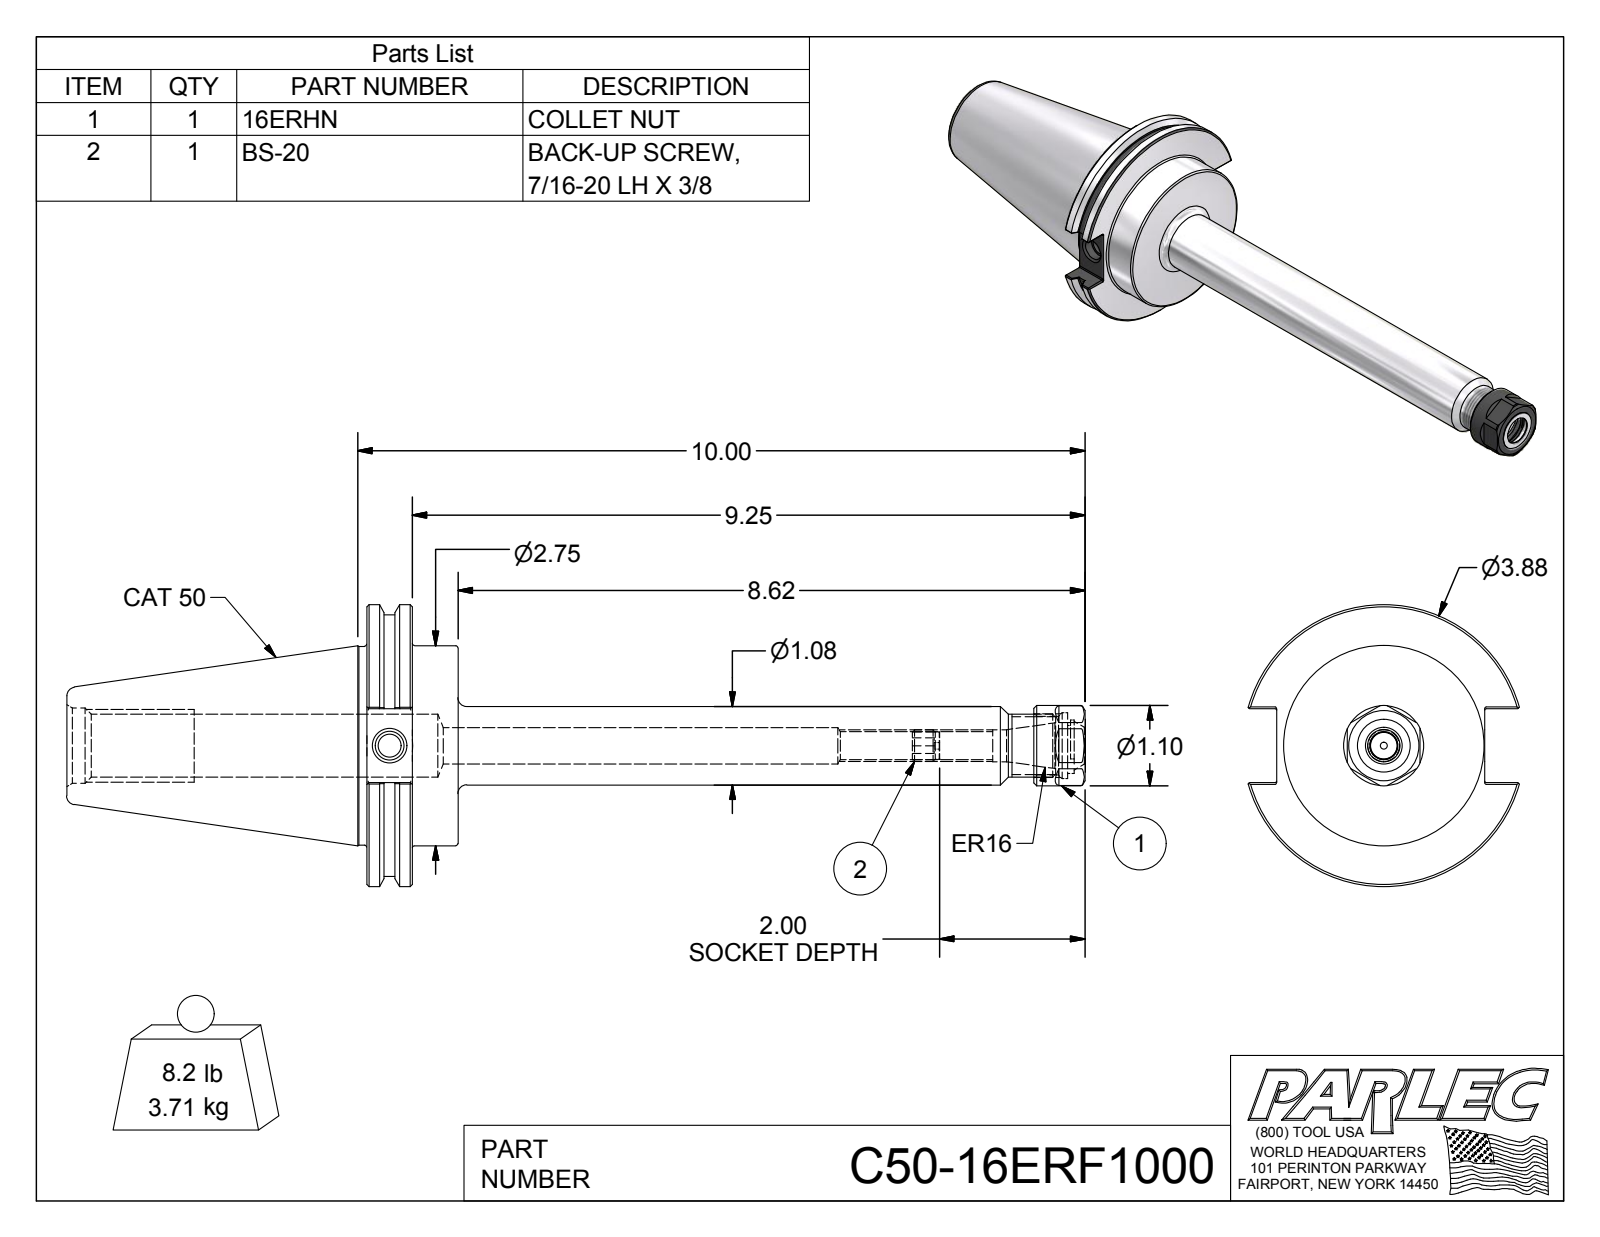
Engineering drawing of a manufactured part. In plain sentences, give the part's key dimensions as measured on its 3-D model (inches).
The part is named "C50-16ER10-1; 16ERHN; BS-20; C50-16ERF1000". Its 3-D file was written by "Autodesk Inventor 2016 (AUTOMOTIVE_DESIGN)". It is 3 solids with 145 faces: 59 planar, 39 cylindrical and 47 other. Overall it measures 14 by 3.875 by 3.729 inches. Its volume is 29.02 cubic inches and its surface area 120.9 square inches. Round holes: 1 of diameter 0.09, 1 of diameter 0.315, 1 of diameter 0.383, 1 of diameter 0.399, 1 of diameter 0.44, 1 of diameter 0.488, 1 of diameter 0.5, 1 of diameter 0.67, 1 of diameter 0.807, 1 of diameter 0.865, 1 of diameter 0.906, 1 of diameter 1.038. Round bosses or shafts: 1 of diameter 3.875, 1 of diameter 3.594, 1 of diameter 2.75, 1 of diameter 2.73, 1 of diameter 1.102, 1 of diameter 1.08, 1 of diameter 0.866, 1 of diameter 0.432. Partial cylindrical surfaces (rounded edges, fillets, slot ends): 12 of radius 0.02, 1 of radius 0.285, 1 of radius 0.354. The main face-to-face distances are 1.255, 0.625, 0.63, 9.875, 9.25, 8.62, 0.99, 4.125, 4.75, 5.38. The hole center spacings are 0.06.
